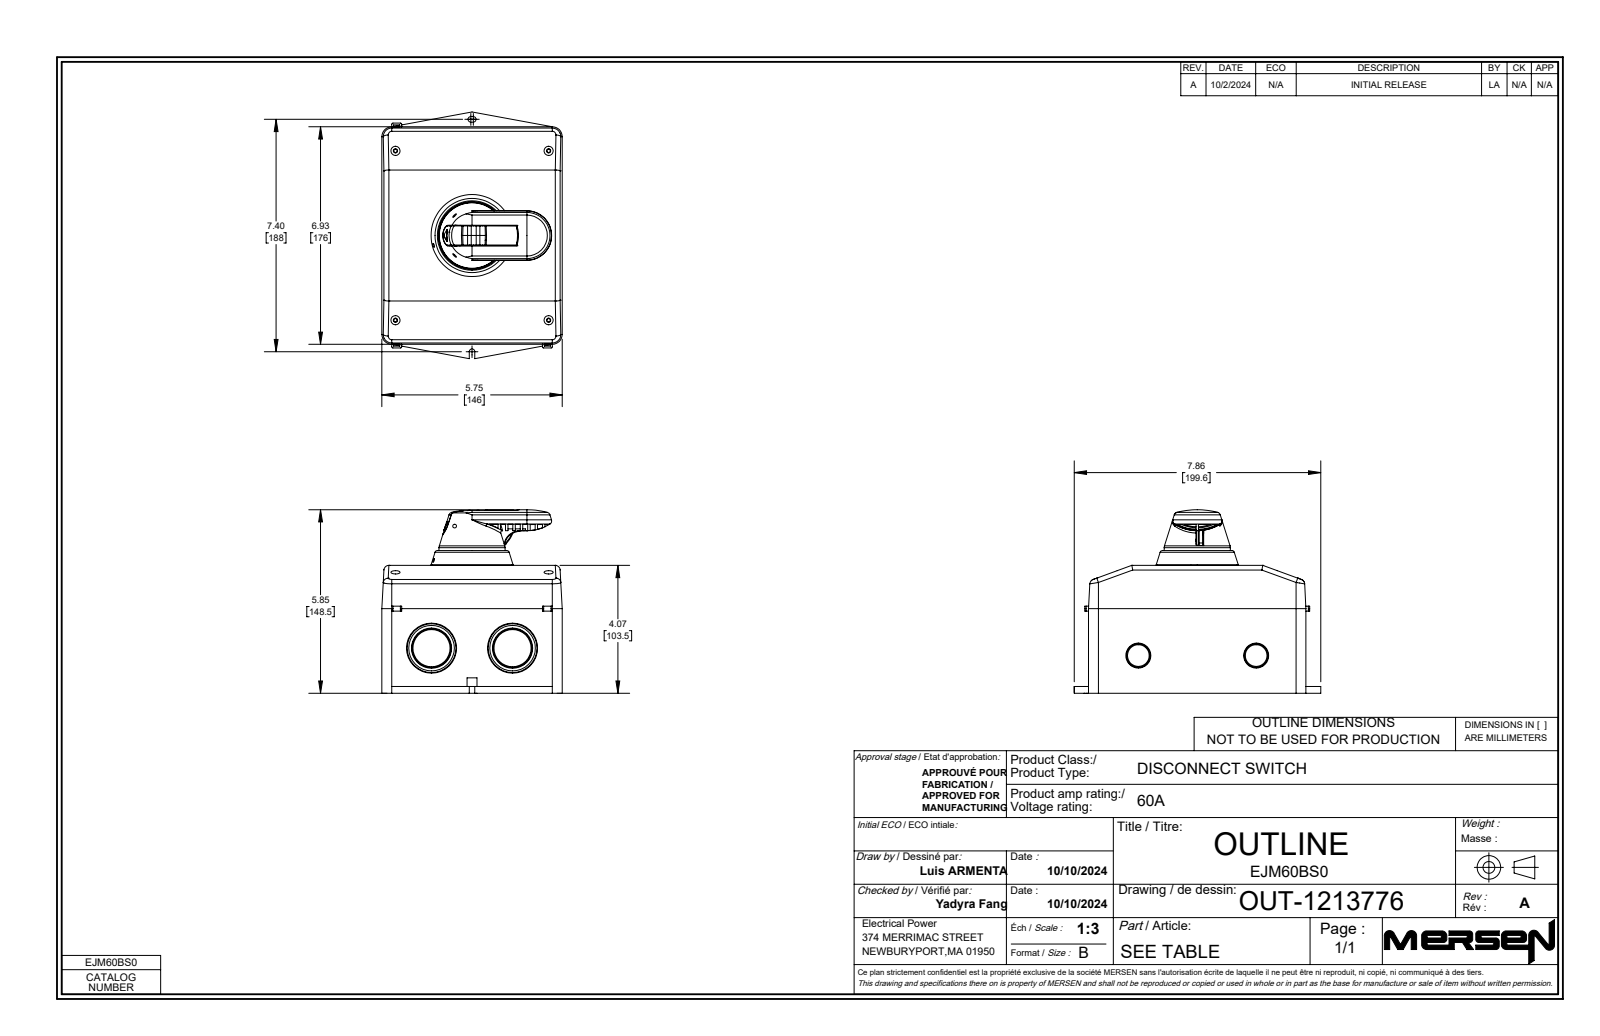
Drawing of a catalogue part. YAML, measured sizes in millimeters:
part_name: "OUT-1213776"
step_written_by: "SolidWorks 2021 (AUTOMOTIVE_DESIGN)"
units: millimeters
bodies: {solids: 0, faces: 1649, planar: 180, cylindrical: 111, other: 1358}
overall_size: [199.59, 148.5, 146]
round_holes:
  - {diameter: 3, count: 1}
  - {diameter: 5.7, count: 1}
  - {diameter: 9, count: 1}
  - {diameter: 10.47, count: 1}
  - {diameter: 26.3, count: 1}
  - {diameter: 50.9, count: 1}
round_bosses_or_shafts:
  - {diameter: 5.6, count: 2}
  - {diameter: 53.5, count: 1}
  - {diameter: 5, count: 1}
partial_cylinders:
  - {radius: 0.5, count: 18}
  - {radius: 0.3, count: 6}
  - {radius: 1, count: 4}
  - {radius: 7.75, count: 4}
  - {radius: 3, count: 2}
  - {radius: 10, count: 2}
  - {radius: 65, count: 2}
  - {radius: 1.6, count: 1}
face_to_face_distances: [6, 4, 12, 2, 18, 10, 8, 16, 24, 14]
hole_center_spacings: [19, 20.21, 20.4, 37.37]
